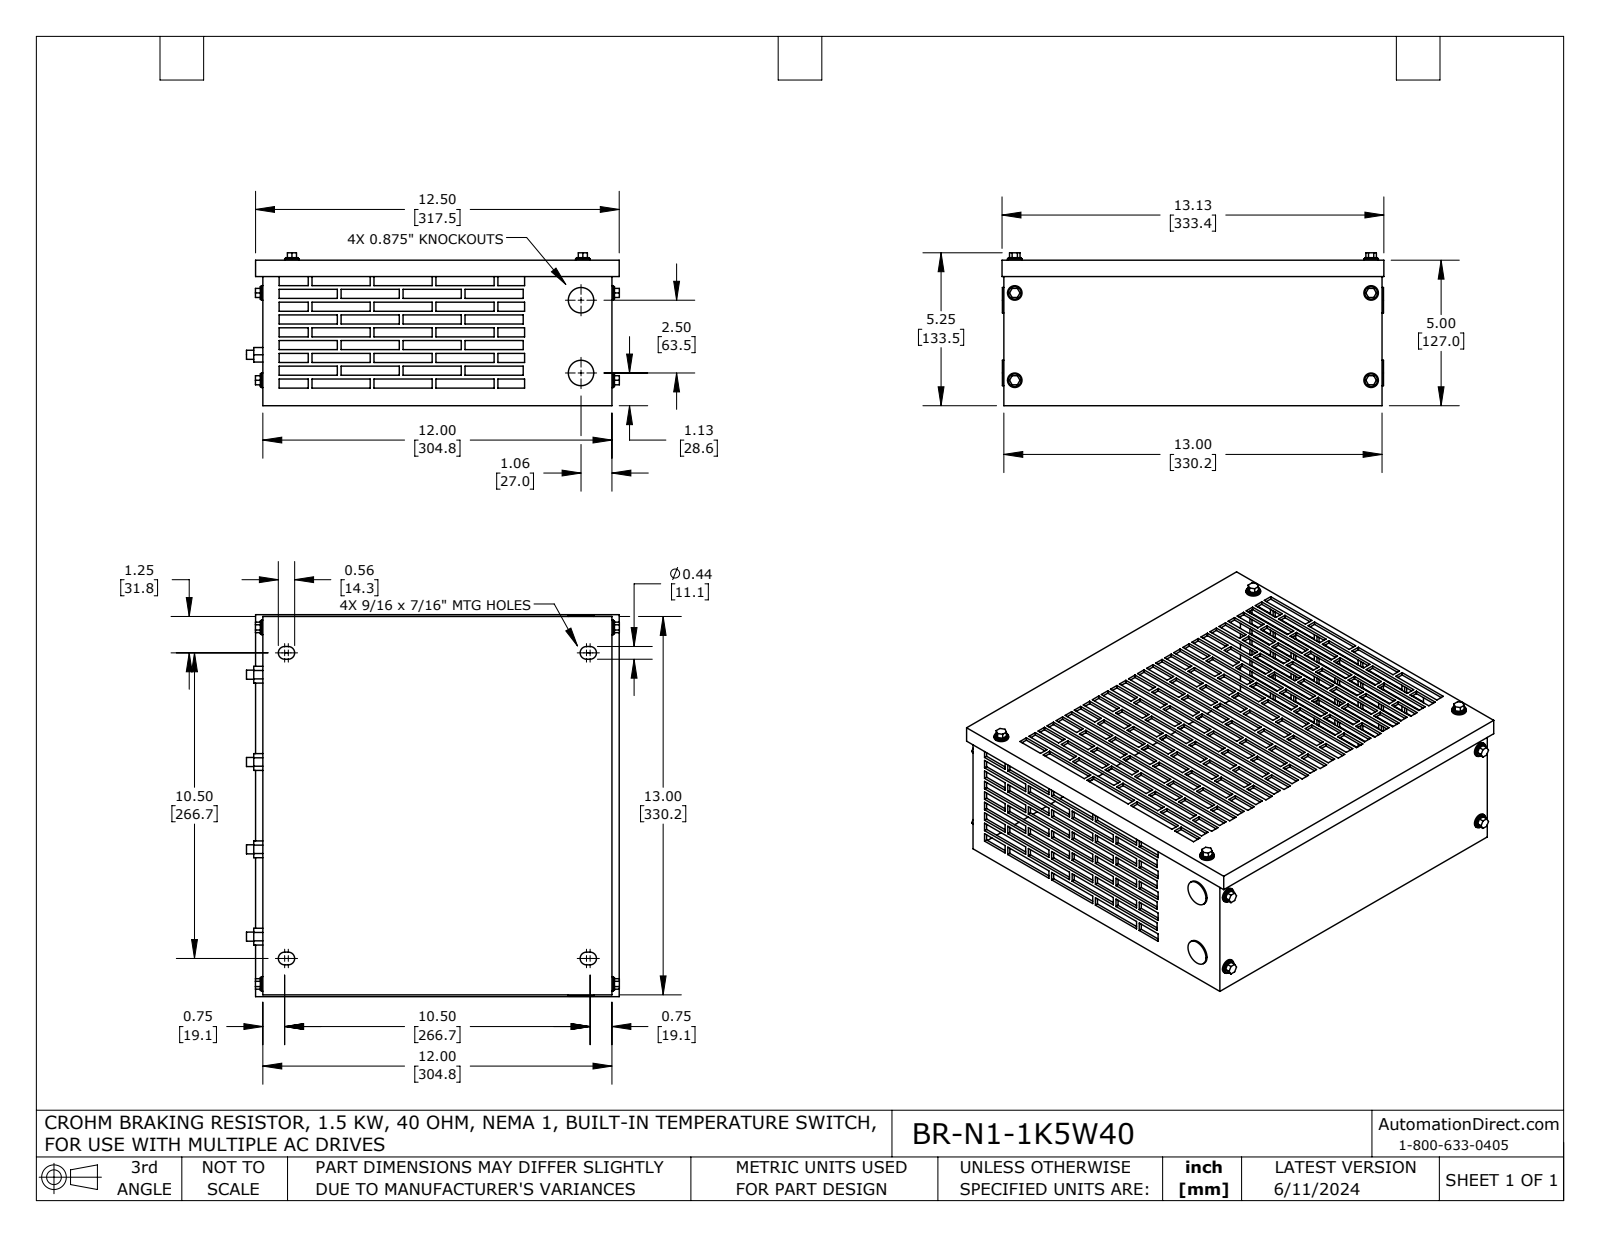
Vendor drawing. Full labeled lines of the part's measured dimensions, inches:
Part name (STEP PRODUCT): BR-N1-1K5W40
STEP written by: SolidWorks 2021 (AUTOMOTIVE_DESIGN)
Units: inches
Bodies: 33 solids, 1136 faces (1032 planar, 104 cylindrical, 0 other)
Overall size (bounding box): 13.125 × 12.817 × 5.254
Volume: 45.79 in³ · Surface area: 1 010 in²
Round holes (diameter × count): ⌀0.25 ×8, ⌀0.75 ×2
Round bosses / shafts (diameter × count): ⌀0.5 ×8, ⌀0.437 ×8, ⌀0.313 ×4, ⌀0.875 ×2
Partial cylindrical surfaces — rounded edges, fillets, slot ends (radius × count): R0.219 ×8
Main face-to-face distances: 0.1, 4.9, 11.9, 5, 4.8, 12, 12.9, 11.8, 13, 12.8
Hole centre spacings: 12.25, 3, 10, 12.611, 15.813, 2.5
